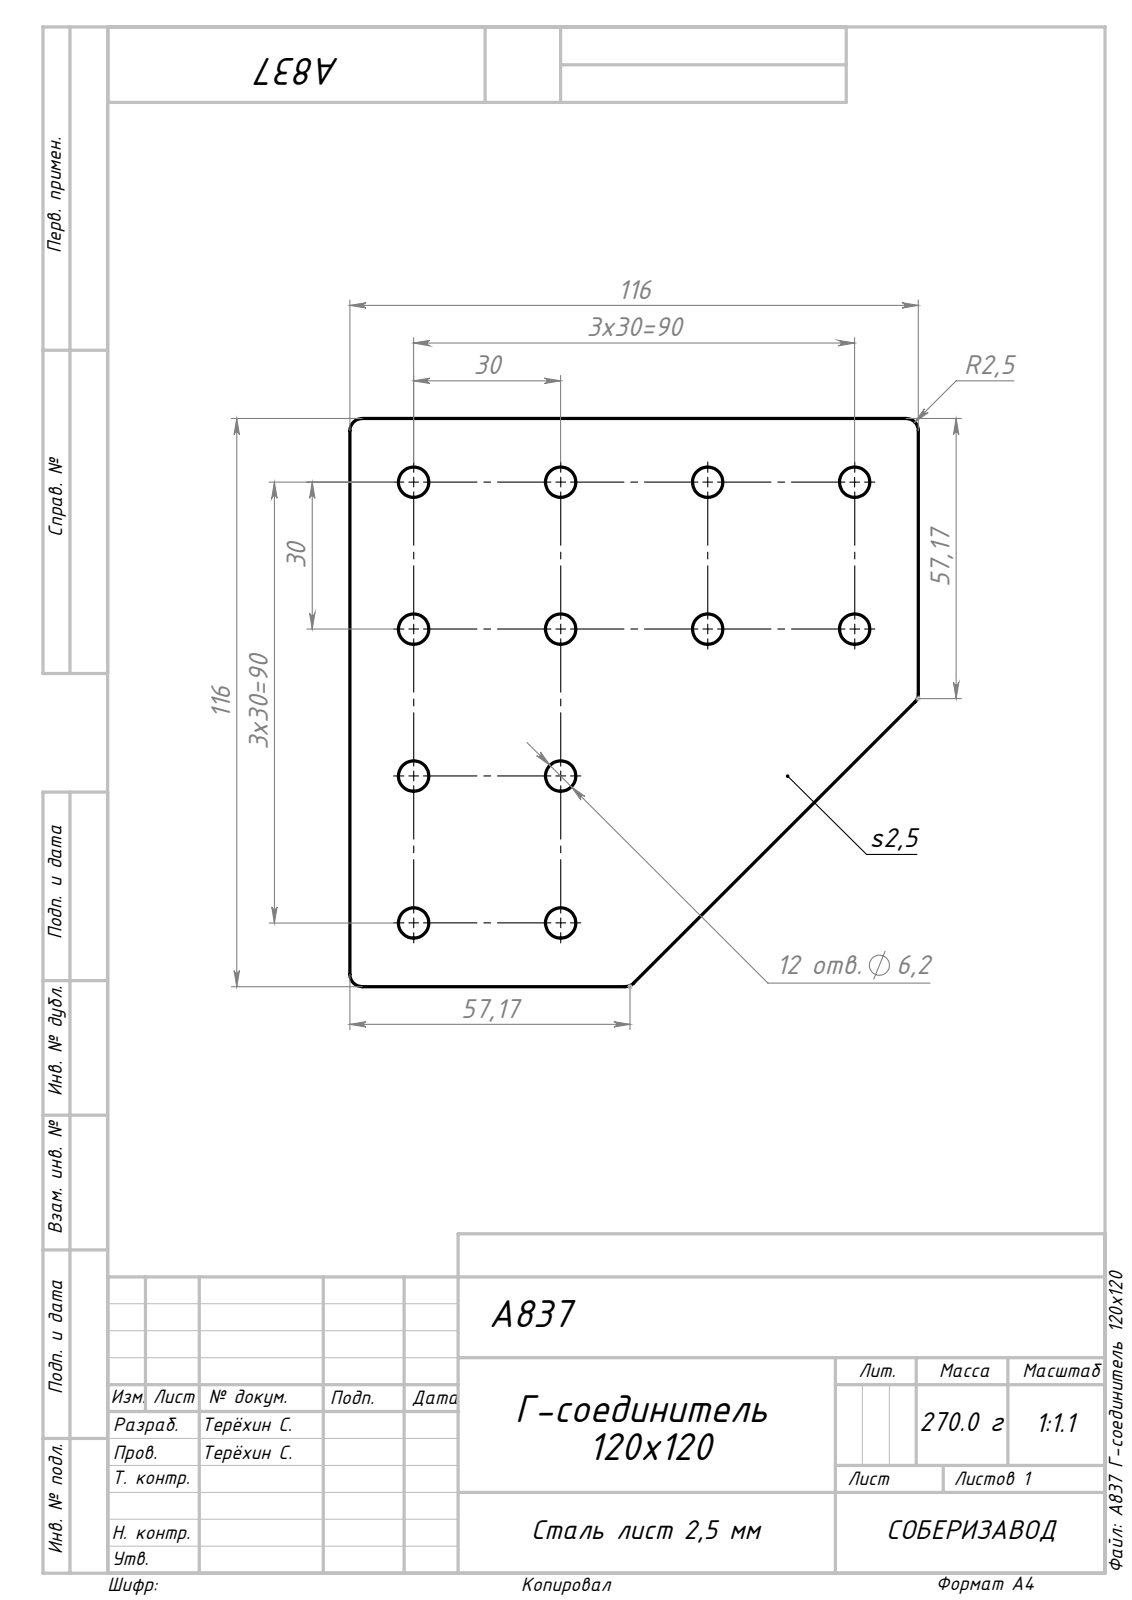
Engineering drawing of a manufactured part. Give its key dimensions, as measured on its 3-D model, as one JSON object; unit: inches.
{"part_name": "Сборка9; A837 Г-соединитель 120х120_00", "step_written_by": "SolidWorks 2022 (AUTOMOTIVE_DESIGN)", "units": "inches", "bodies": {"solids": 1, "faces": 36, "planar": 7, "cylindrical": 29, "other": 0}, "overall_size": [4.567, 4.567, 0.098], "volume_in3": 1.733, "surface_area_in2": 37.77, "round_holes": [[0.244, 12]], "partial_cylinders_radius": [[0.098, 5]], "face_to_face_distances": [0.098, 4.567], "hole_center_spacings": [1.181, 2.641, 1.67, 2.362, 3.735, 3.341, 3.543, 4.259]}
